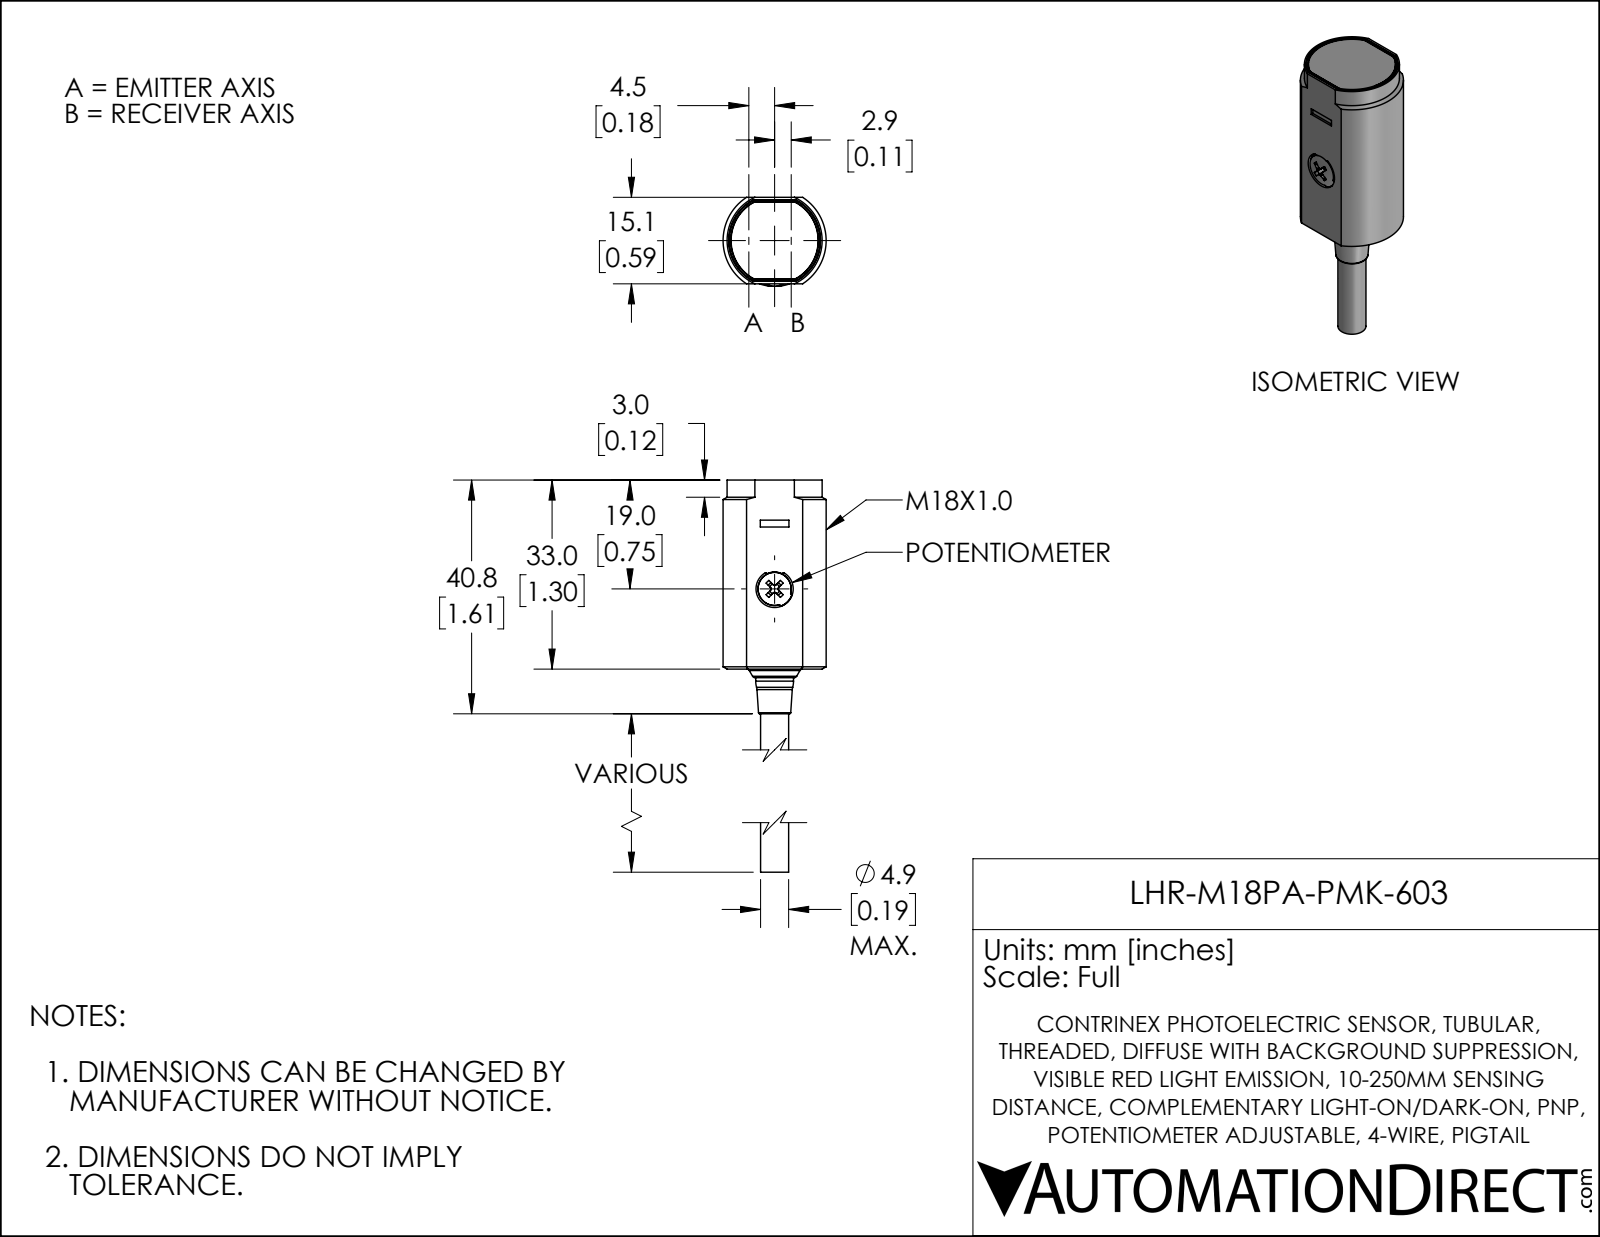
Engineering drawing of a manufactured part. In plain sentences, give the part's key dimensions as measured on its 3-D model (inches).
The part is named "LHR-M18PA-PMK-603". Its 3-D file was written by "SolidWorks 2021 (AUTOMOTIVE_DESIGN)". It is 1 solid with 116 faces: 58 planar, 40 cylindrical and 18 other. Overall it measures 2.205 by 0.709 by 0.611 inches. Its volume is 0.5 cubic inches and its surface area 4.262 square inches. Round holes: 1 of diameter 0.256. Round bosses or shafts: 1 of diameter 0.26, 1 of diameter 0.193. Partial cylindrical surfaces (rounded edges, fillets, slot ends): 8 of radius 0.014, 8 of radius 0.028, 4 of radius 0.006, 4 of radius 0.024, 1 of radius 0.116, 1 of radius 0.299, 1 of radius 0.302, 1 of radius 0.313. The main face-to-face distances are 0.594, 1.297, 0.016, 1.299, 2.205, 2.203, 0.906, 0.579, 0.563, 0.014.
